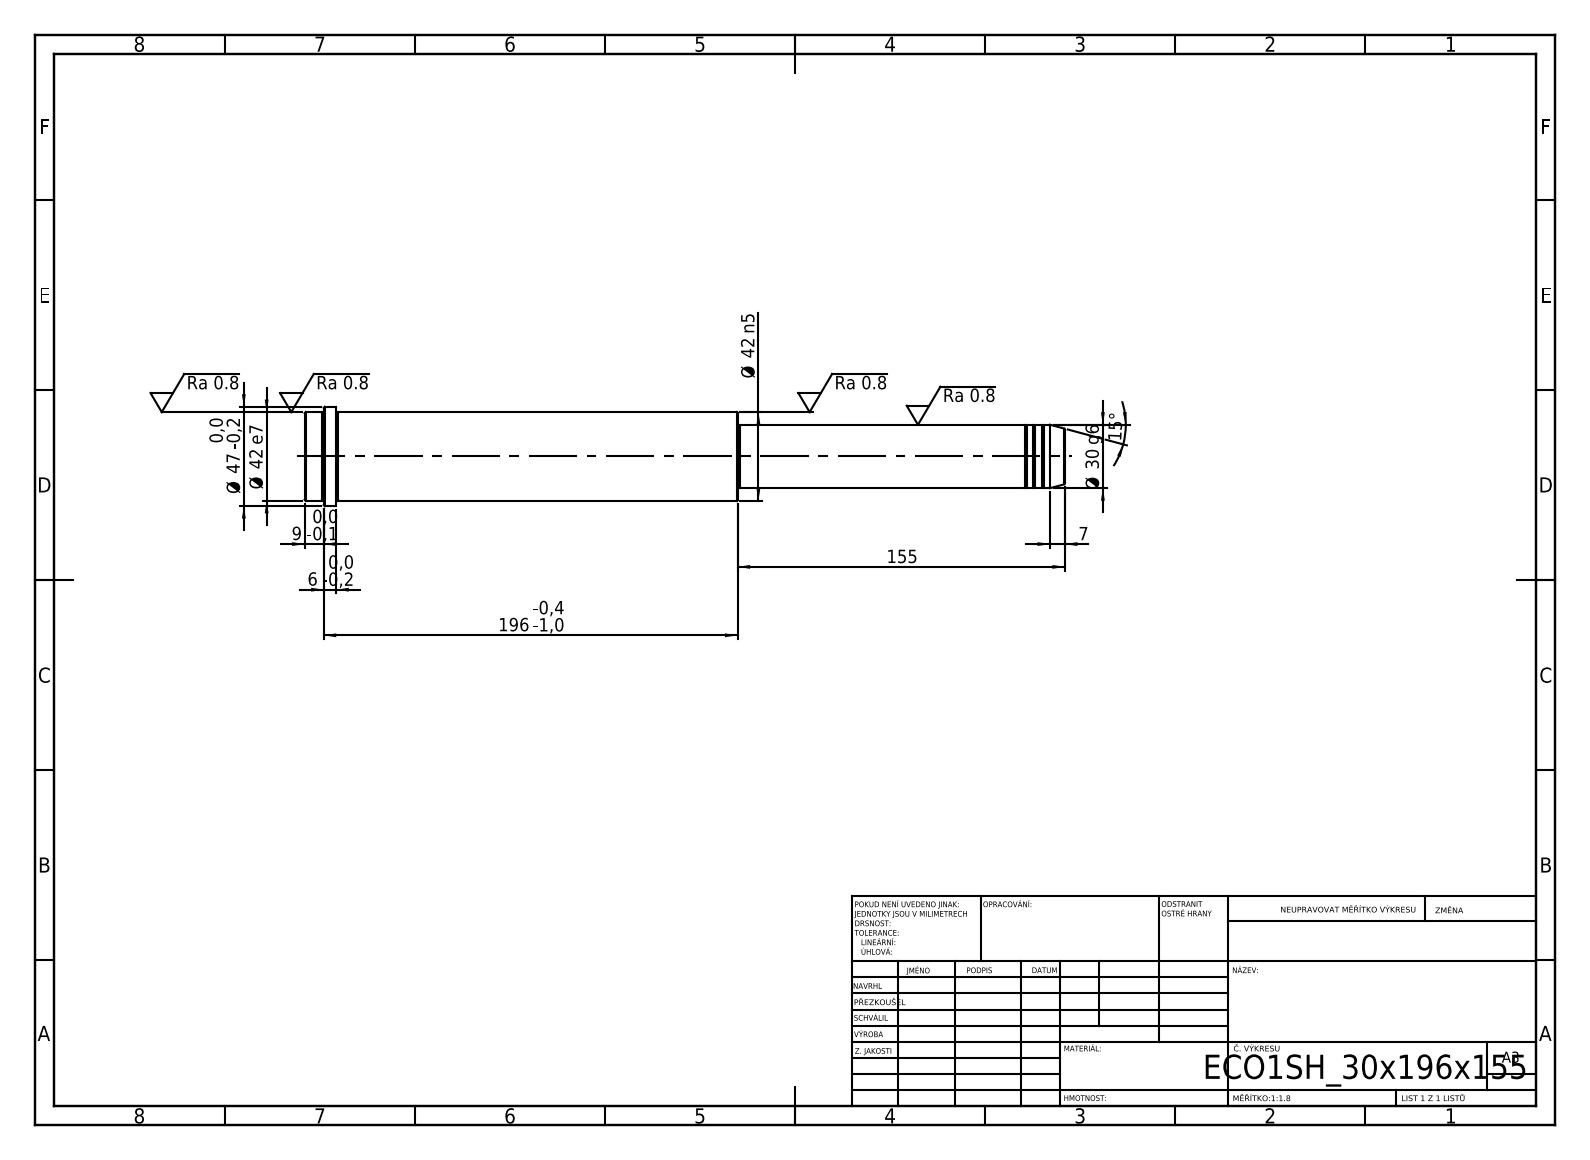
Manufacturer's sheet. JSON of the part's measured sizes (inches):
{"step_written_by": "SolidWorks 2019 (CONFIG_CONTROL_DESIGN)", "units": "inches", "bodies": {"solids": 1, "faces": 52, "planar": 6, "cylindrical": 16, "other": 30}, "overall_size": [14.173, 1.85, 1.85], "volume_in3": 24.09, "surface_area_in2": 70.2, "round_bosses_or_shafts": [[1.85, 1], [1.654, 1], [1.181, 1], [1.142, 1]], "face_to_face_distances": [8.071, 6.102, 14.173, 13.583, 7.48, 0.591, 13.819, 7.717, 0.236, 0.354]}
